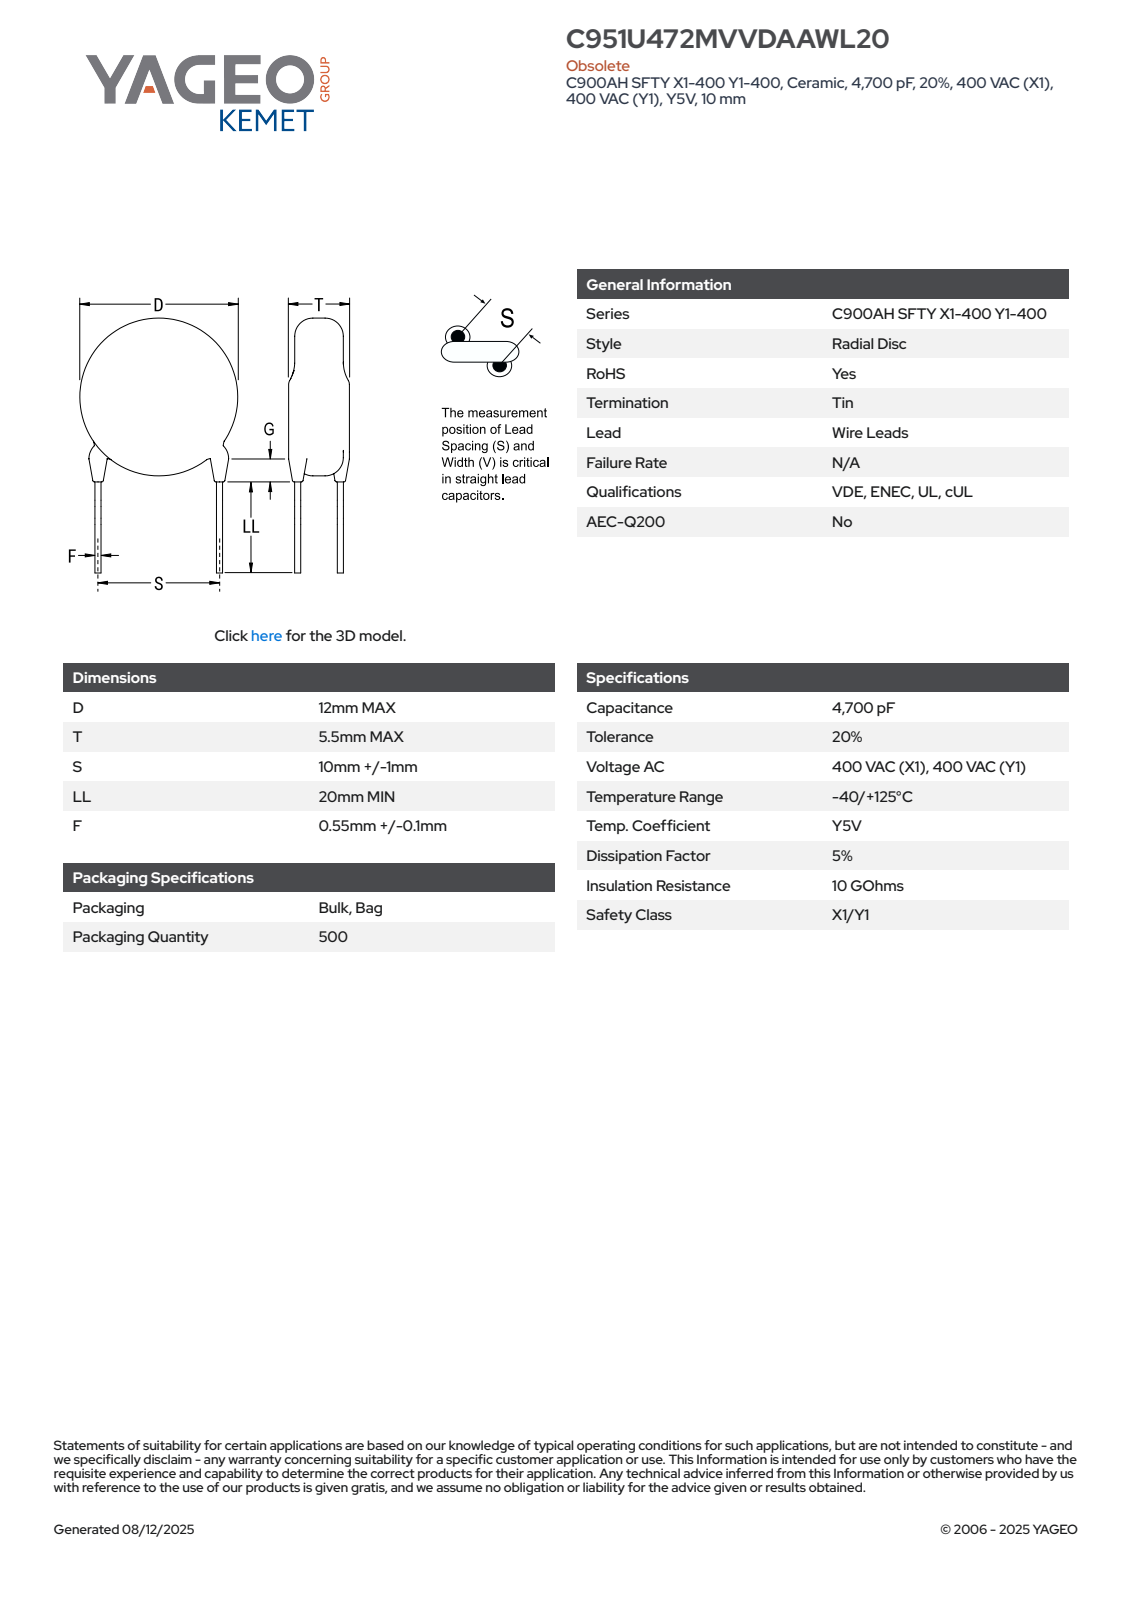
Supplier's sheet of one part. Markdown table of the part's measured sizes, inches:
| quantity | value |
| --- | --- |
| part name | CCD_STC900_D12T5.5S10LL20F0.65G3 |
| STEP written by | SolidWorks 2014 (AUTOMOTIVE_DESIGN) |
| units | inches |
| bodies | 4 solids, 83 faces (61 planar, 6 cylindrical, 16 other) |
| overall size | 1.272 × 0.472 × 0.217 |
| volume | 0.038 in³ |
| surface area | 0.783 in² |
| round bosses / shafts (diameter × count) | 0.026 × 2, 0.472 × 1 |
| main face-to-face distances | 0.217, 1.063, 1.009, 0.054, 0.015, 0.013, 0.024, 0.223, 0.044, 0.034 |
